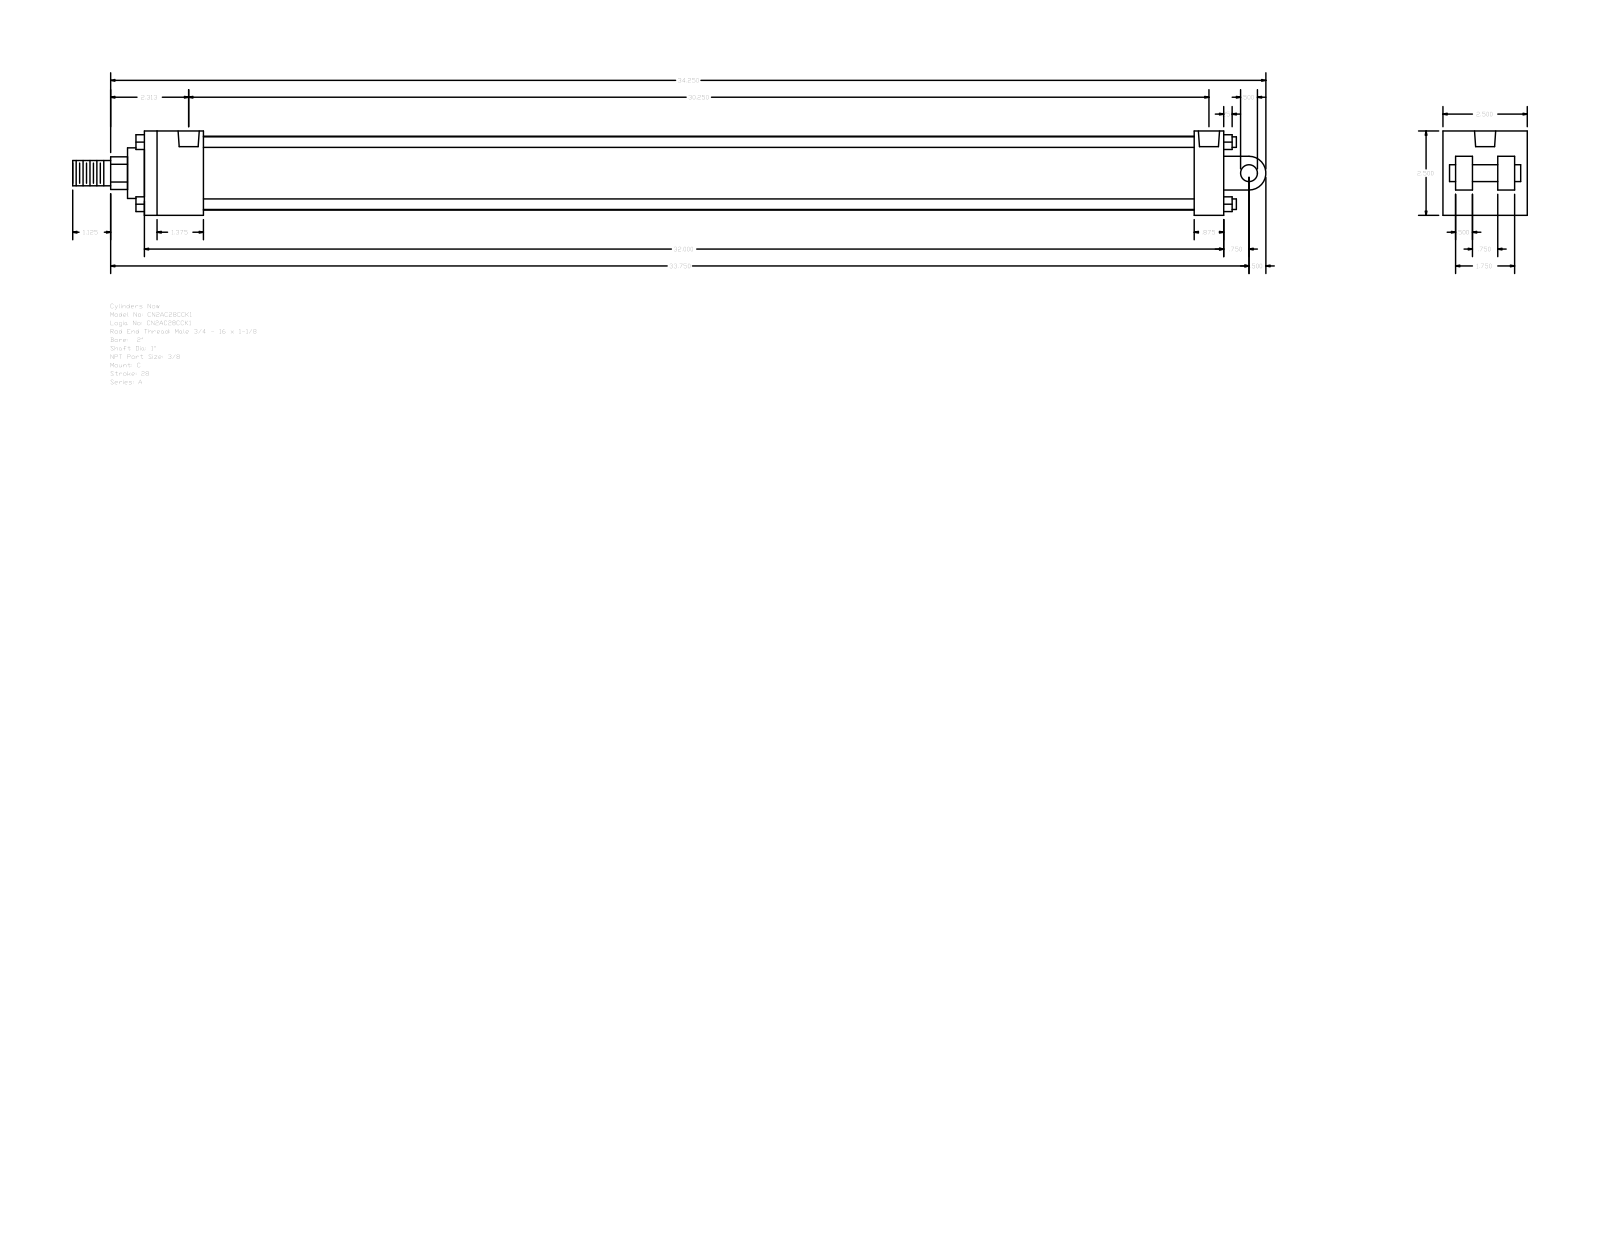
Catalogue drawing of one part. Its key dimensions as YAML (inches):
part_name: "A_C__0200_1"
step_written_by: "GSSL Pune (CONFIG_CONTROL_DESIGN)"
units: inches
bodies: {solids: 0, faces: 135, planar: 102, cylindrical: 33, other: 0}
overall_size: [35.375, 2.5, 2.5]
round_holes:
  - {diameter: 0.219, count: 4}
  - {diameter: 0.627, count: 2}
round_bosses_or_shafts:
  - {diameter: 0.313, count: 4}
  - {diameter: 2.19, count: 1}
  - {diameter: 1.5, count: 1}
  - {diameter: 1, count: 1}
  - {diameter: 0.75, count: 1}
  - {diameter: 0.5, count: 1}
partial_cylinders:
  - {radius: 0.484, count: 1}
  - {radius: 0.5, count: 1}
face_to_face_distances: [2.5, 0.875, 32, 1.75, 0.5, 30.25, 31.125, 29.375, 0.375, 2.125]
hole_center_spacings: [30.031, 0.063, 0.157, 30.093, 30.187, 30.25]
